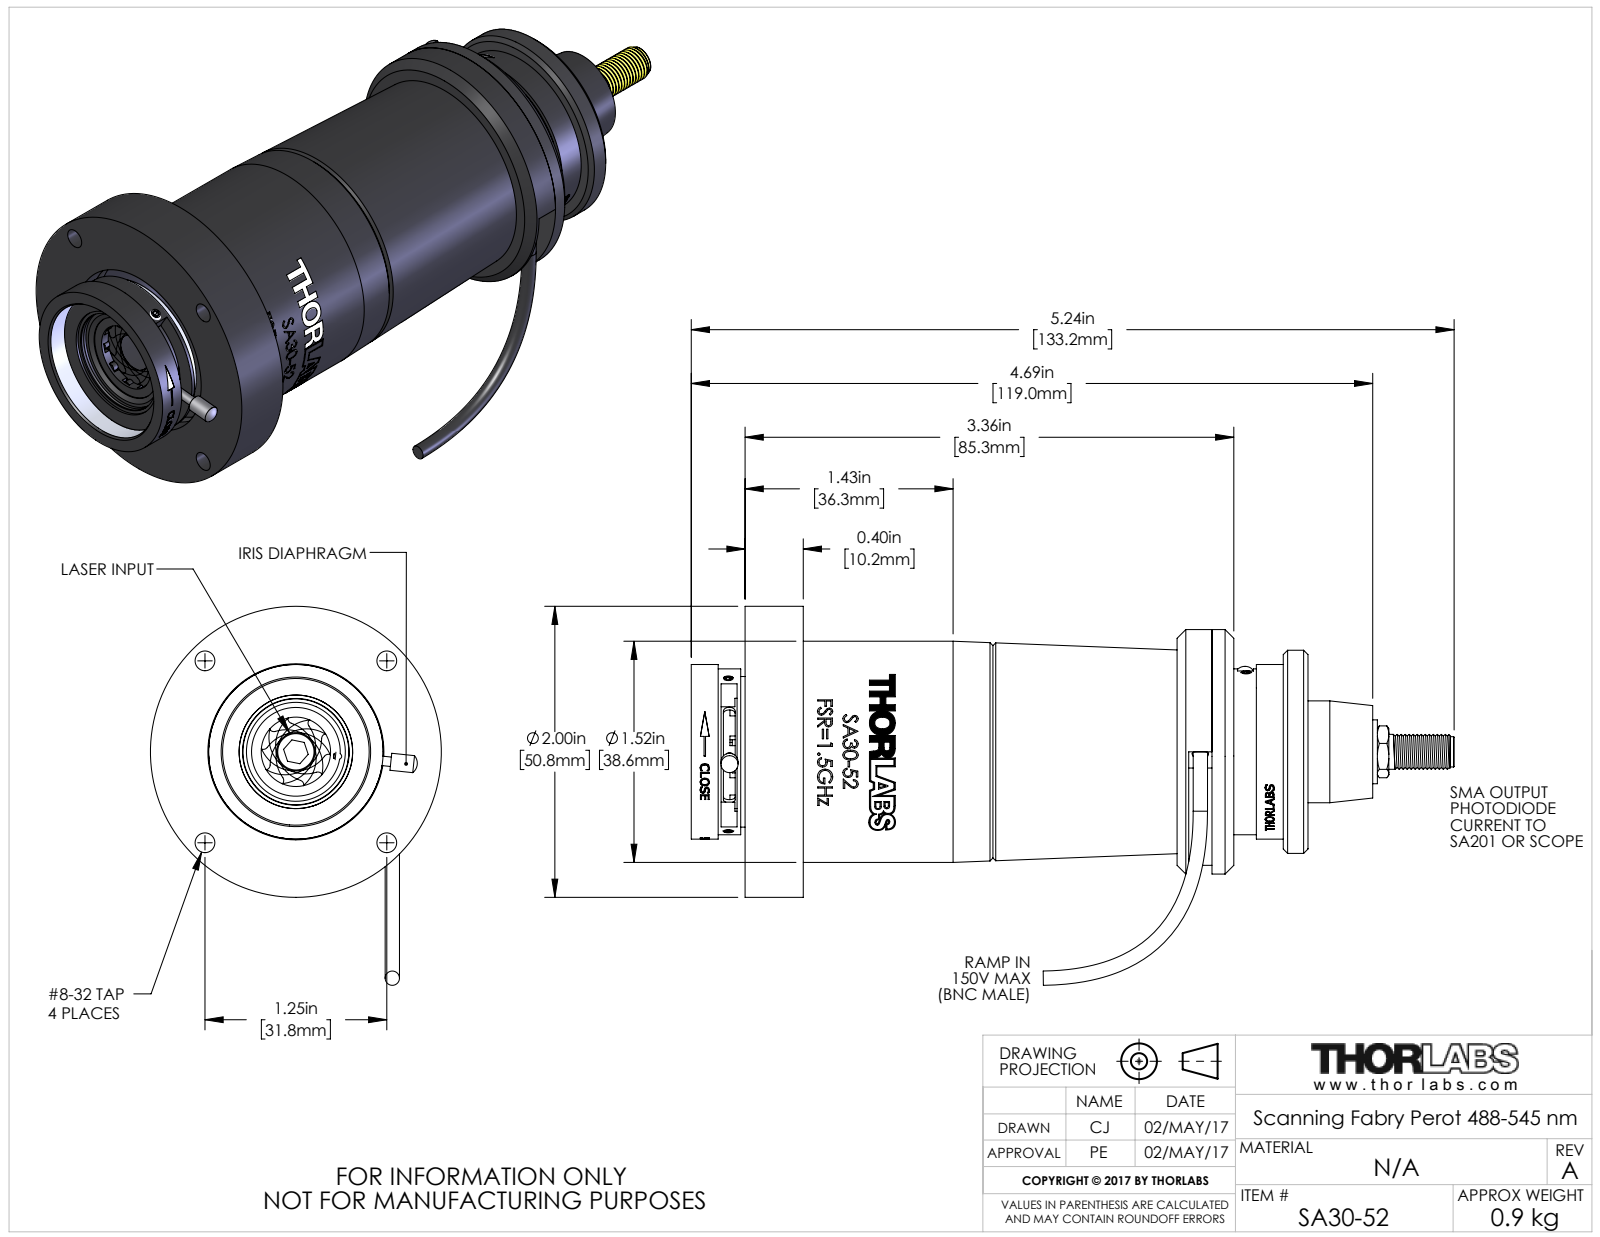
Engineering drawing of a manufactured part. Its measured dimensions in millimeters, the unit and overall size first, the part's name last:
Units: millimetres
Overall size (bounding box): 133.21 × 66.16 × 50.8
Round holes (diameter × count): ⌀1.68 ×20, ⌀3.45 ×4, ⌀1.1 ×2, ⌀1.6 ×2, ⌀1 ×1, ⌀2.87 ×1, ⌀4.6 ×1, ⌀6.35 ×1, ⌀8.26 ×1, ⌀9.78 ×1, ⌀10.16 ×1, ⌀12.04 ×1
Round bosses / shafts (diameter × count): ⌀1.52 ×20, ⌀1.65 ×14, ⌀1.65 ×8, ⌀2.18 ×4, ⌀2.98 ×2, ⌀1.63 ×2, ⌀50.8 ×1, ⌀42.67 ×1
Partial cylindrical surfaces — rounded edges, fillets, slot ends (radius × count): R0.83 ×20, R0.85 ×20, R1.61 ×20, R6.38 ×20, R9.6 ×20, R0.62 ×2, R3.3 ×2, R25.4 ×2
Main face-to-face distances: 81.53, 86.82, 10.16, 3.81, 98.29, 16.76, 71.37, 88.13, 85.34, 75.18
Hole centre spacings: 14.11, 12, 8.72, 4.58, 14.1, 14.83, 8.71, 7.41
Volume: 54 432 mm³ · Surface area: 45 769 mm²
Bodies: 41 solids, 1534 faces (609 planar, 511 cylindrical, 414 other)
Part name (STEP PRODUCT): SW3dPS-SMA Washer; SM05PD1A-Diode Cover; SA210-16-CT; SW3dPS-sma bulkhead straight jack (+7 more)
STEP written by: SolidWorks 2016 (AUTOMOTIVE_DESIGN)
